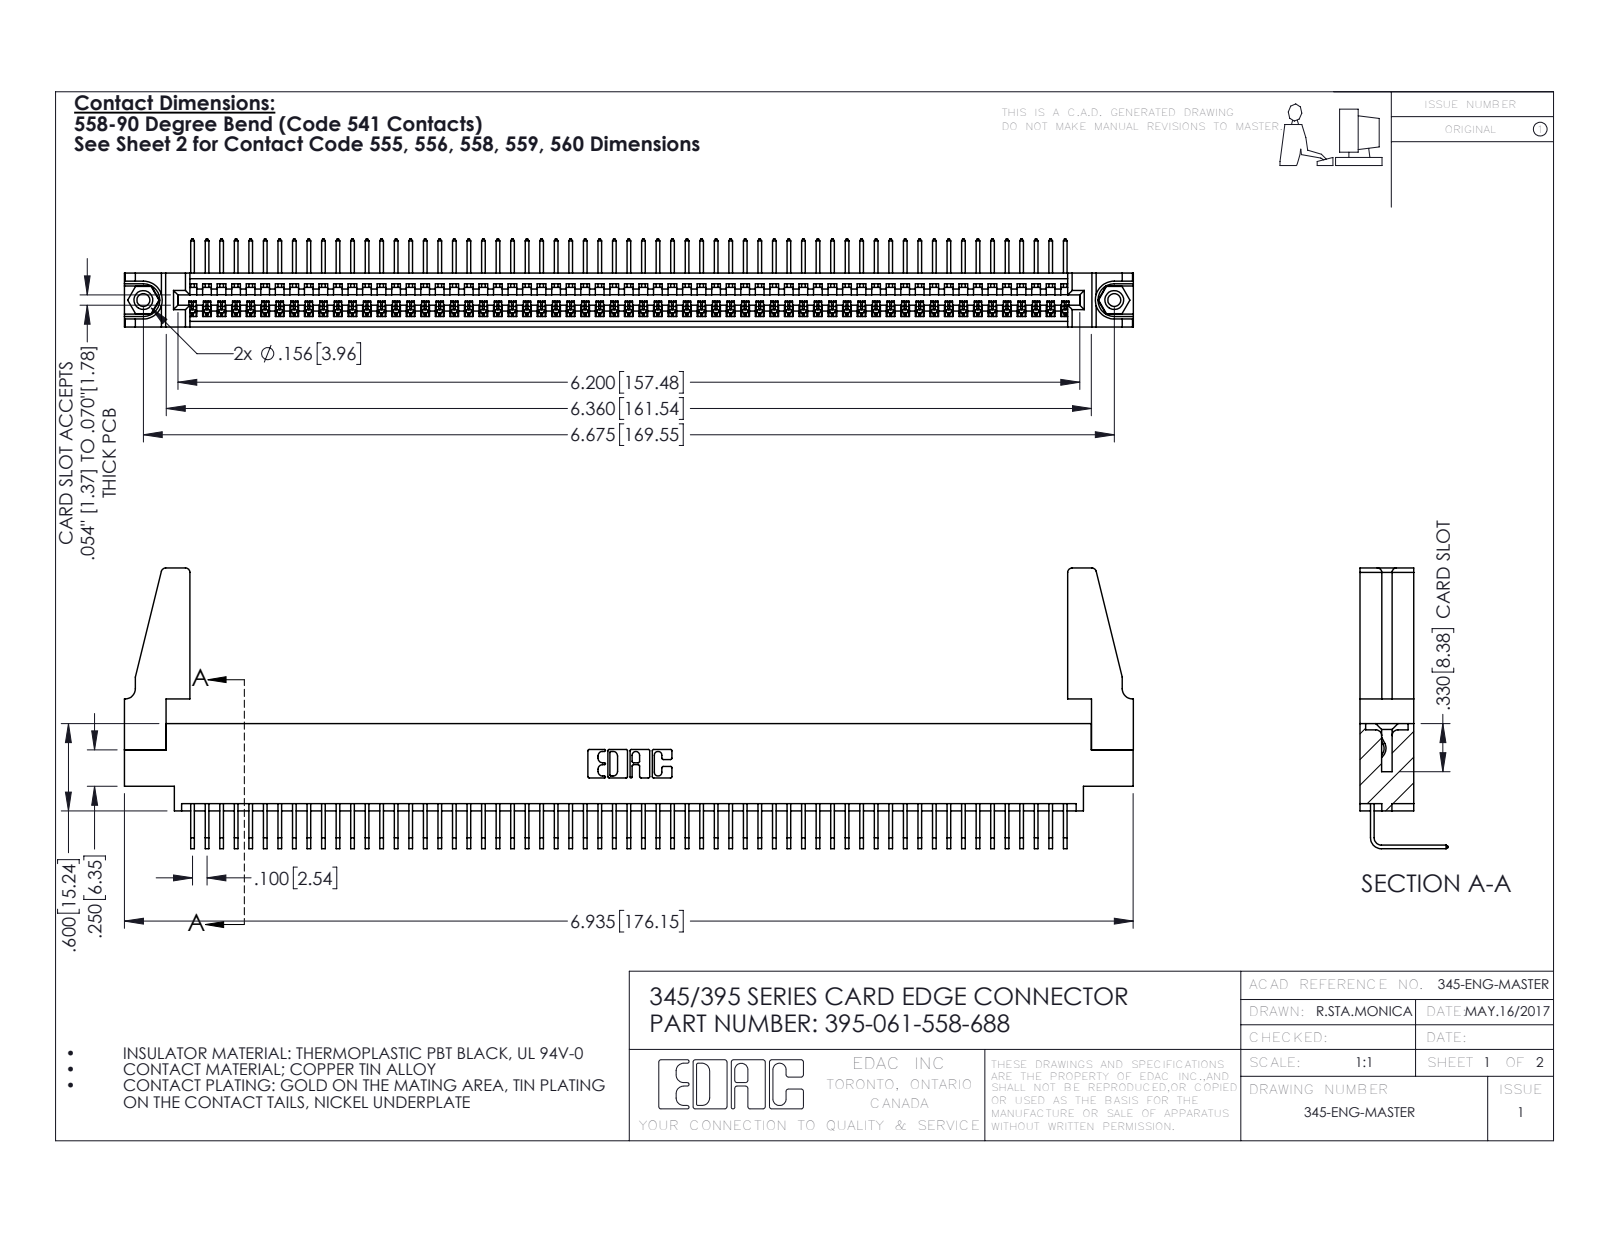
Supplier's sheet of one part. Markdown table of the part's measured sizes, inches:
| quantity | value |
| --- | --- |
| part name | 345-292-001_558 Tail - 2; 345-220-078_345-220-088; 345-250-001_345-250-001-102; 395-061-558-688 (+1 more) |
| STEP written by | SolidWorks 2016 (CONFIG_CONTROL_DESIGN) |
| units | inches |
| bodies | 66 solids, 3914 faces (2718 planar, 1180 cylindrical, 16 other) |
| overall size | 6.936 × 1.929 × 0.605 |
| volume | 1.235 in³ |
| surface area | 42.27 in² |
| round holes (diameter × count) | 0.089 × 2, 0.125 × 2, 0.156 × 2, 0.064 × 1 |
| round bosses / shafts (diameter × count) | 0.155 × 2 |
| partial cylindrical surfaces (radius × count) | 0.006 × 122, 0.01 × 22, 0.03 × 8, 0.007 × 6, 0.031 × 6, 0.026 × 3, 0.031 × 2, 0.04 × 2 |
| main face-to-face distances | 0.072, 0.298, 0.37, 0.098, 0.272, 0.025, 0.2, 0.225, 0.175, 0.149 |
| hole center spacings | 0.27, 6.439, 6.675 |
